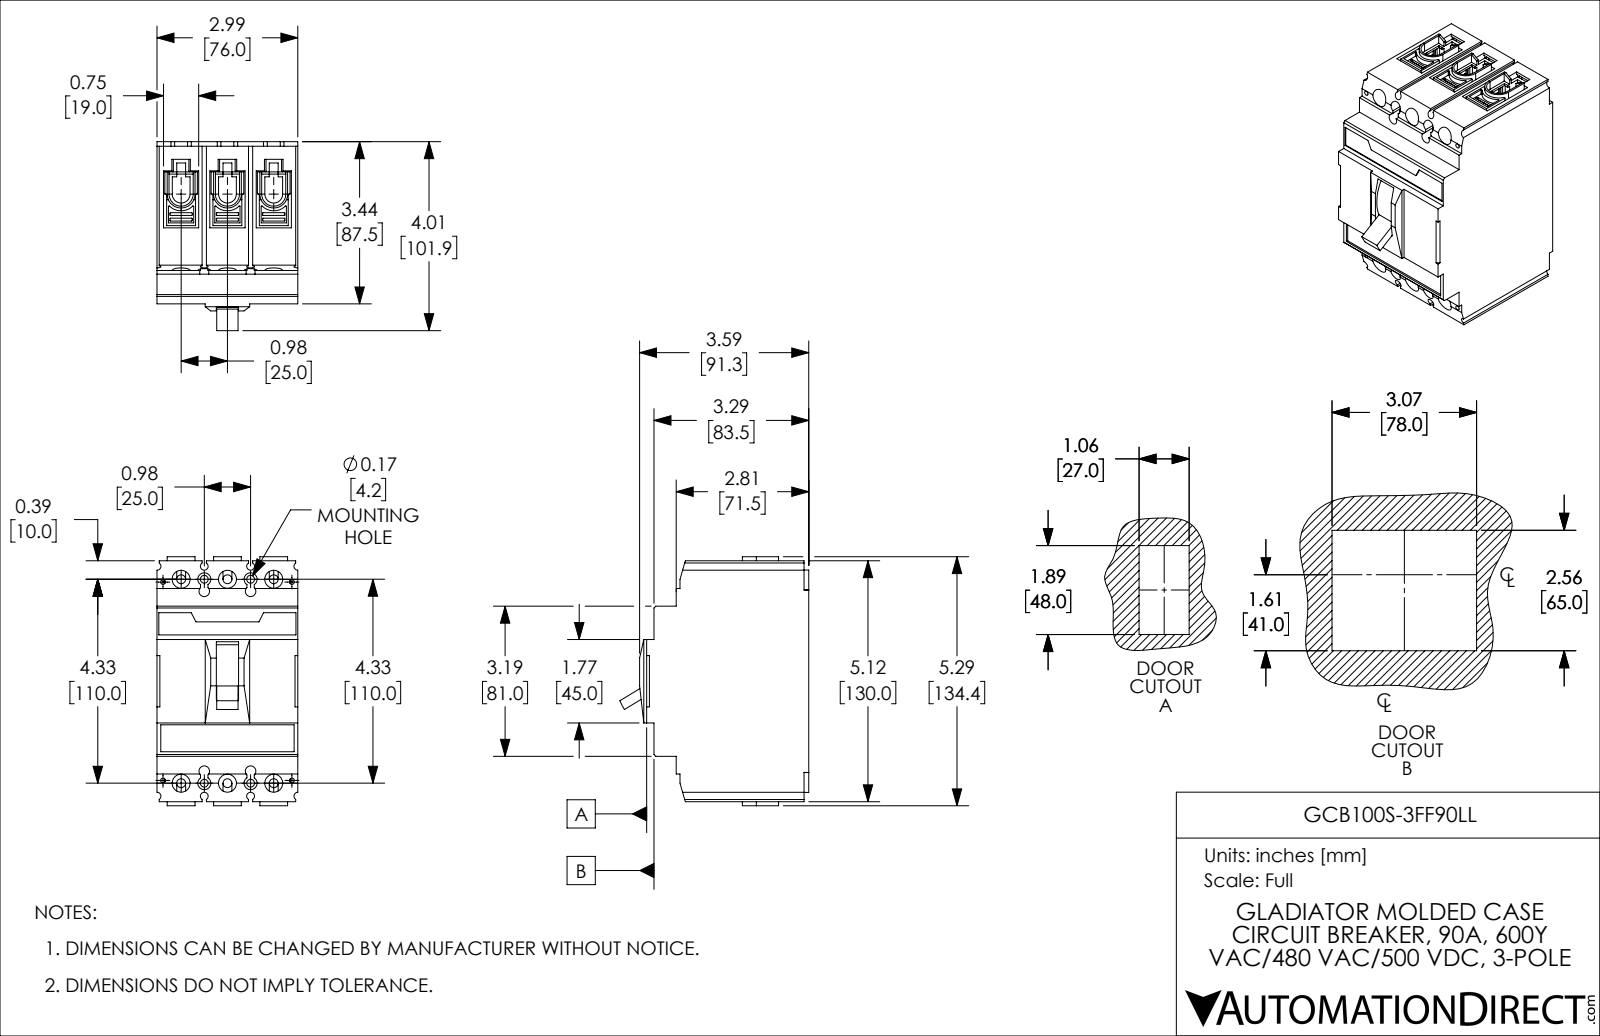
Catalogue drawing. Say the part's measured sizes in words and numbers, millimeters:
The part is named "GCB100S-3FF90LL". Its 3-D file was written by "SolidWorks 2021 (CONFIG_CONTROL_DESIGN)". It is 1 solid with 1256 faces: 784 planar, 424 cylindrical and 48 other. Overall it measures 134.4 by 101.9 by 76 millimeters. Its volume is 708 400 cubic millimeters and its surface area 95 810 square millimeters. Round holes: 8 of diameter 4.2, 6 of diameter 4.8, 6 of diameter 9.7, 4 of diameter 2.5, 4 of diameter 7. Partial cylindrical surfaces (rounded edges, fillets, slot ends): 86 of radius 0.3, 38 of radius 0.5, 14 of radius 1, 14 of radius 4, 6 of radius 0.6, 4 of radius 2.1, 4 of radius 2.8, 3 of radius 4.8. The main face-to-face distances are 76, 25, 15.8, 114.2, 44, 2.8, 87.5, 19, 50, 130. The hole center spacings are 12.5, 14.3, 25, 110.7, 117.7, 112.8, 110, 7.
